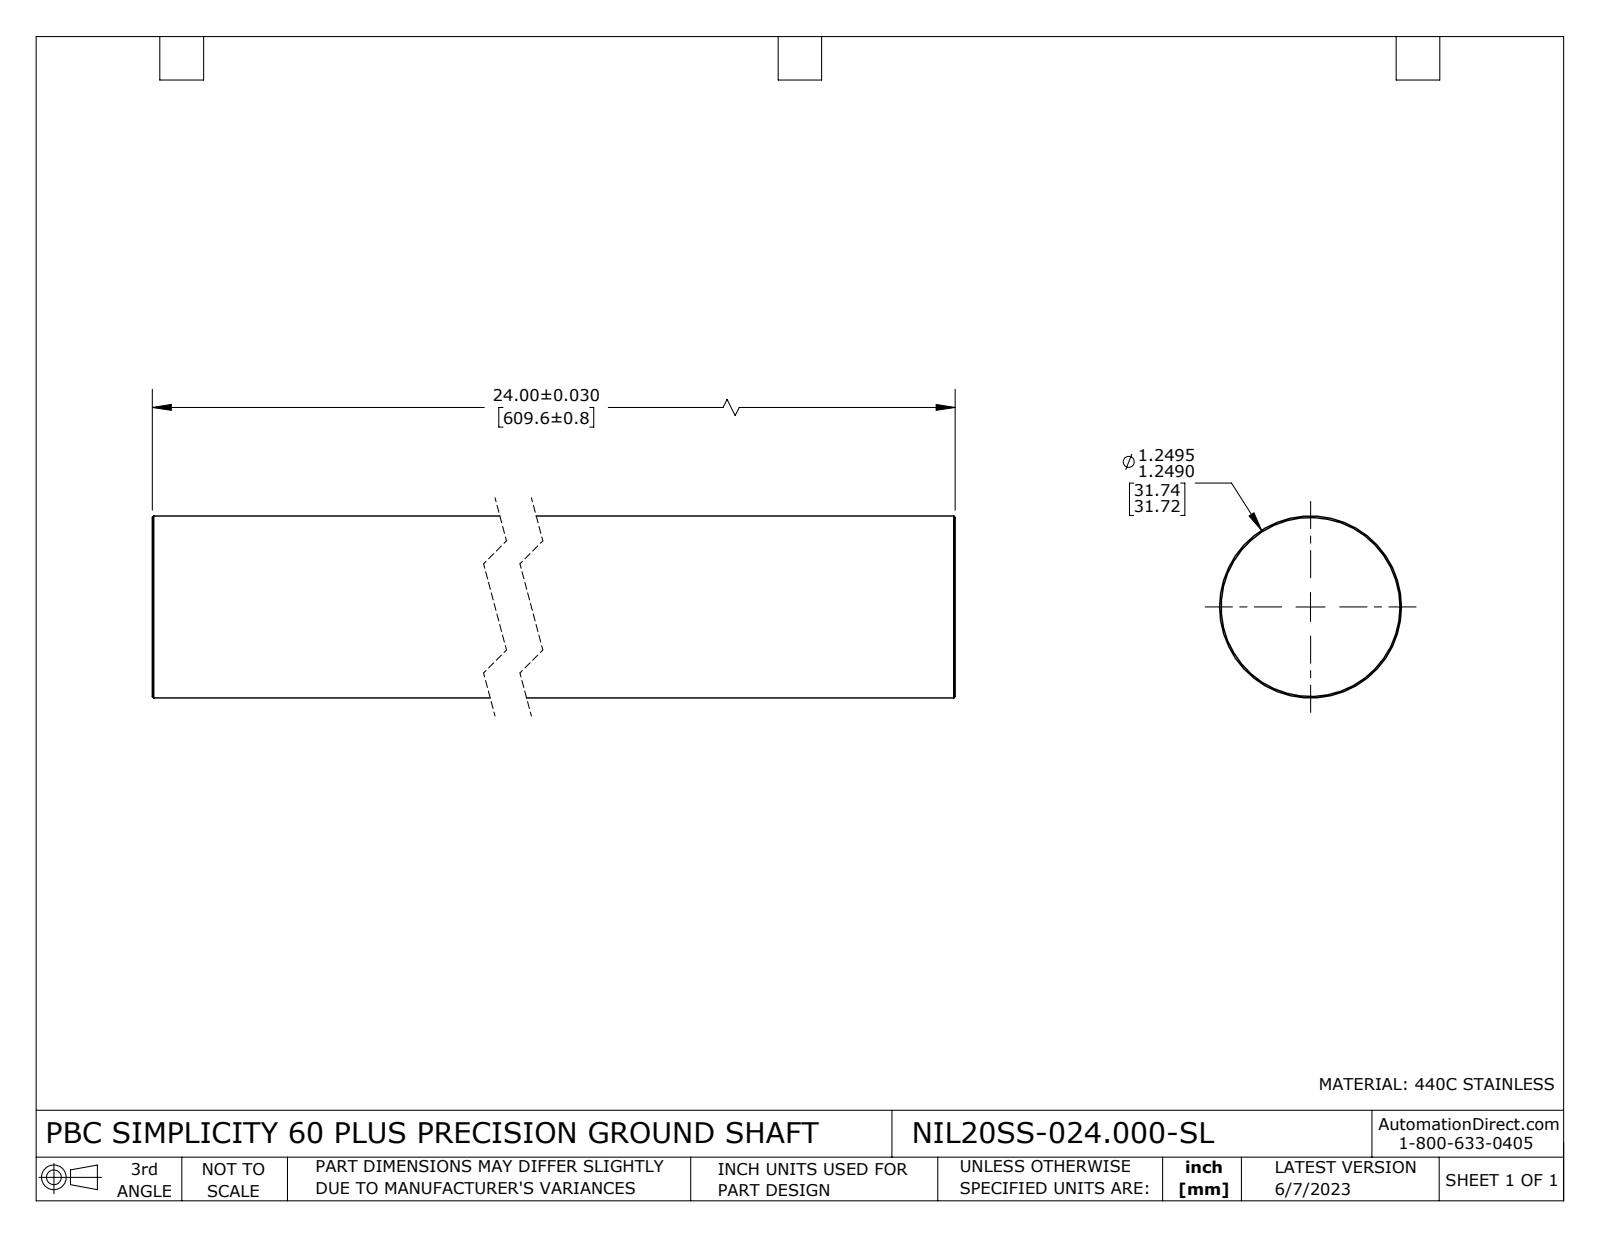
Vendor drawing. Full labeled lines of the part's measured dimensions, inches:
Part name (STEP PRODUCT): NIL20SS-024.000-SL
STEP written by: SolidWorks 2021 (CONFIG_CONTROL_DESIGN)
Units: inches
Bodies: 1 solid, 8 faces (2 planar, 2 cylindrical, 4 other)
Overall size (bounding box): 24 × 1.25 × 1.25
Volume: 29.45 in³ · Surface area: 96.66 in²
Round bosses / shafts (diameter × count): ⌀1.25 ×1
Main face-to-face distances: 24
